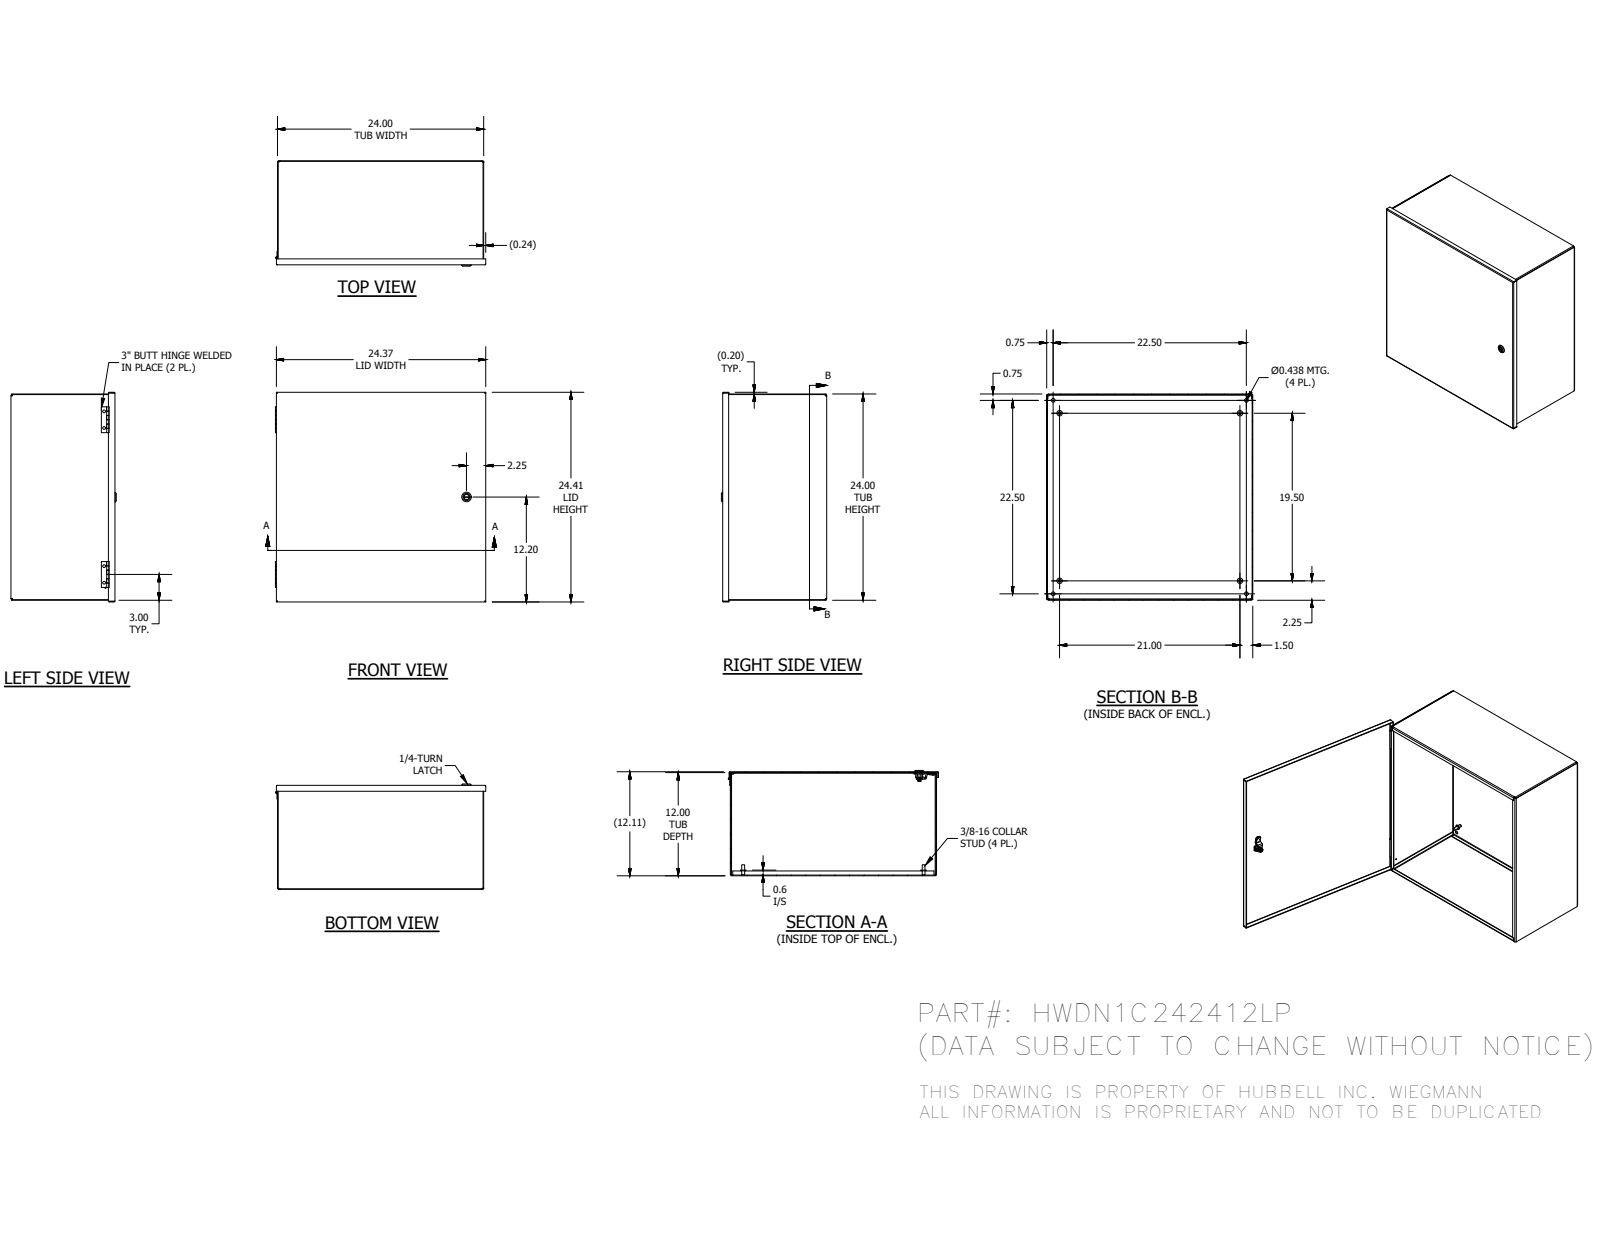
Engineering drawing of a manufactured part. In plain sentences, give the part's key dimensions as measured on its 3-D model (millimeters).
The part is named "N1C242412LPBLR; N1C2412LPTB; N1C2424LPLID; 1000-101-GPF_GPD (+8 more)". Its 3-D file was written by "Autodesk Inventor 2016 (AUTOMOTIVE_DESIGN)". It is 21 solids with 717 faces: 437 planar, 212 cylindrical and 68 other. Overall it measures 622.01 by 619.92 by 330.52 millimeters. Its volume is 3 084 000 cubic millimeters and its surface area 3 298 000 square millimeters. Round holes: 4 of diameter 7.95, 4 of diameter 11.11, 1 of diameter 3.05, 1 of diameter 3.3, 1 of diameter 5, 1 of diameter 8, 1 of diameter 10, 1 of diameter 10.2, 1 of diameter 16.1, 1 of diameter 20.38. Round bosses or shafts: 4 of diameter 15.88, 4 of diameter 8.38, 1 of diameter 28, 1 of diameter 27, 1 of diameter 23, 1 of diameter 19.8, 1 of diameter 15.8, 1 of diameter 15.2. Partial cylindrical surfaces (rounded edges, fillets, slot ends): 30 of radius 0.3, 12 of radius 1.59, 12 of radius 3.47, 10 of radius 0.5, 4 of radius 0.79, 4 of radius 2.67, 4 of radius 4, 3 of radius 0.4. The main face-to-face distances are 1.88, 607.72, 324.64, 605.84, 609.6, 322.76, 326.52, 321.97, 2.67, 5.16. The hole center spacings are 571.5, 49.28, 287.54, 457.2, 610.47, 808.22, 15.51, 64.39.
